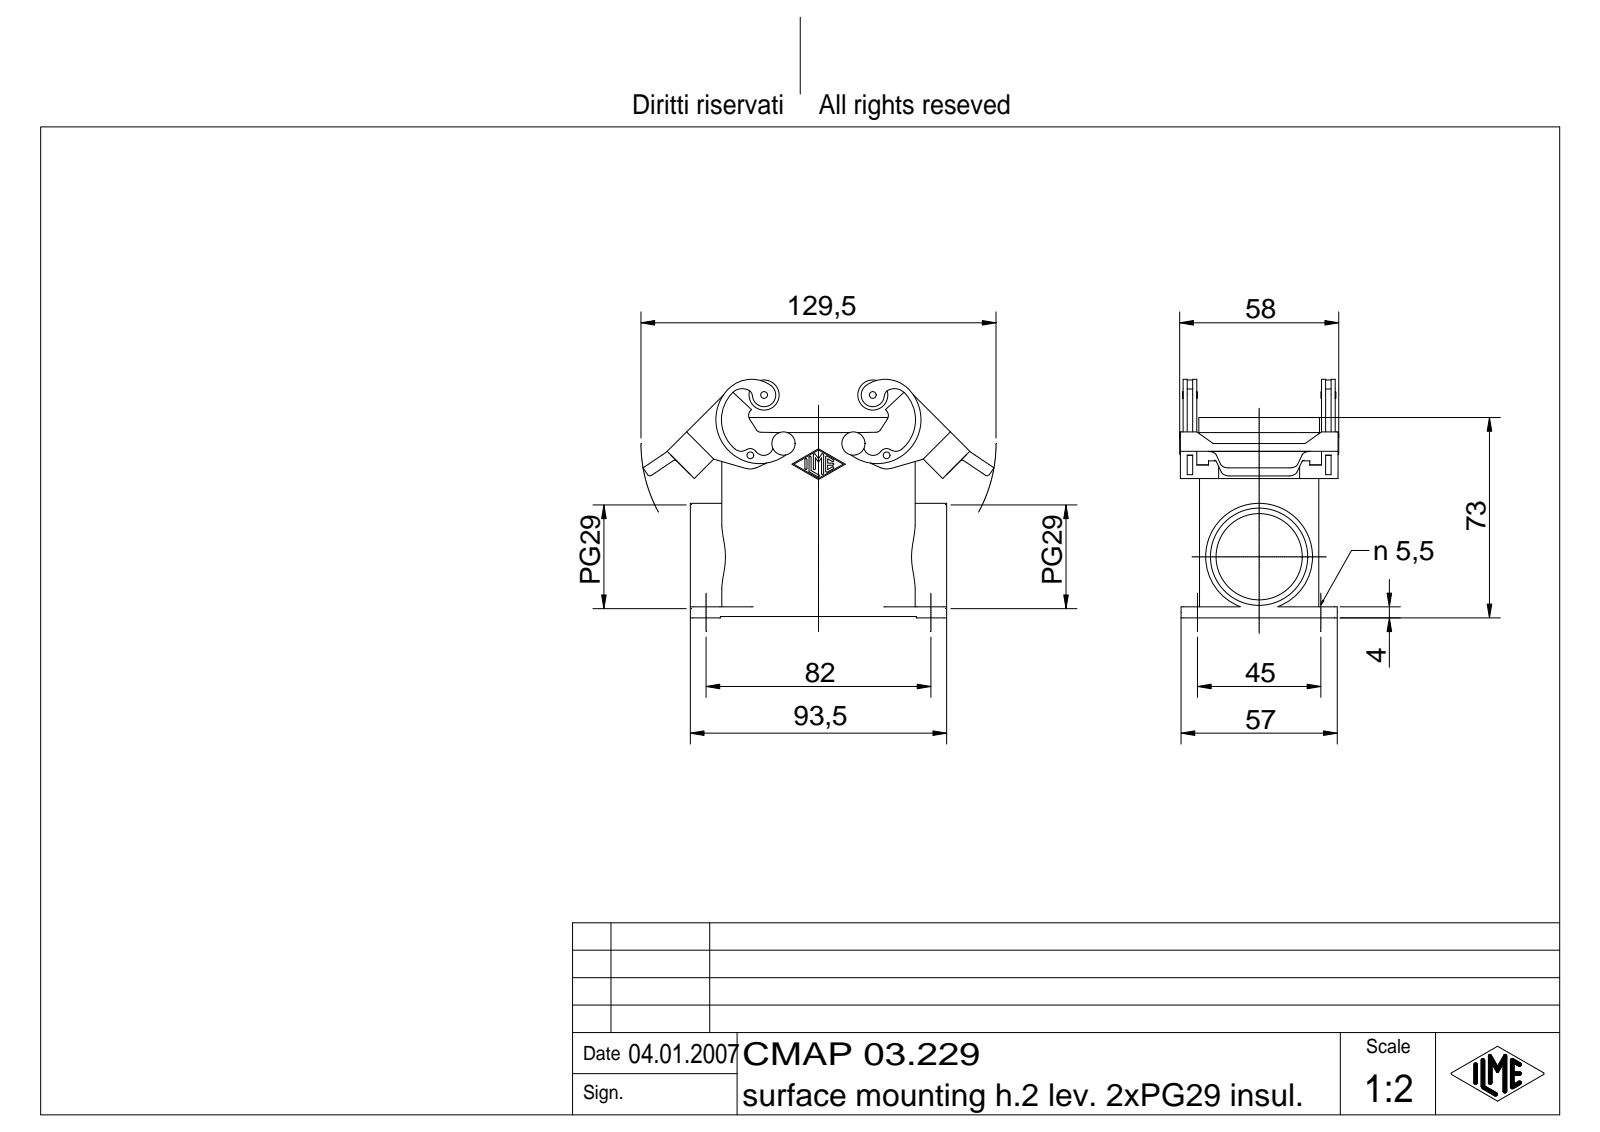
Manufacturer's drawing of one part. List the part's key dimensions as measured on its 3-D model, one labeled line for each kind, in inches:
Part name (STEP PRODUCT): CMAP 03.229
STEP written by: Autodesk Inventor 7 (AUTOMOTIVE_DESIGN)
Units: inches
Bodies: 1 solid, 752 faces (193 planar, 207 cylindrical, 352 other)
Overall size (bounding box): 5.039 × 3.423 × 2.283
Volume: 5.866 in³ · Surface area: 90.94 in²
Round holes (diameter × count): ⌀0.079 ×4, ⌀0.217 ×4, ⌀0.098 ×2, ⌀1.239 ×1, ⌀1.397 ×1
Round bosses / shafts (diameter × count): ⌀0.433 ×2, ⌀0.197 ×2, ⌀0.118 ×2, ⌀1.535 ×1
Partial cylindrical surfaces — rounded edges, fillets, slot ends (radius × count): R0.039 ×20, R0.015 ×14, R0.118 ×12, R0.236 ×8, R0.098 ×6, R0.059 ×4, R0.079 ×4, R0.138 ×4
Main face-to-face distances: 0.118, 1.594, 1.713, 0.138, 1.476, 0.157, 1.988, 0.03, 0.177, 0.098
Hole centre spacings: 0.888, 1.772, 1.96, 3.228, 3.683, 1.561, 1.956
